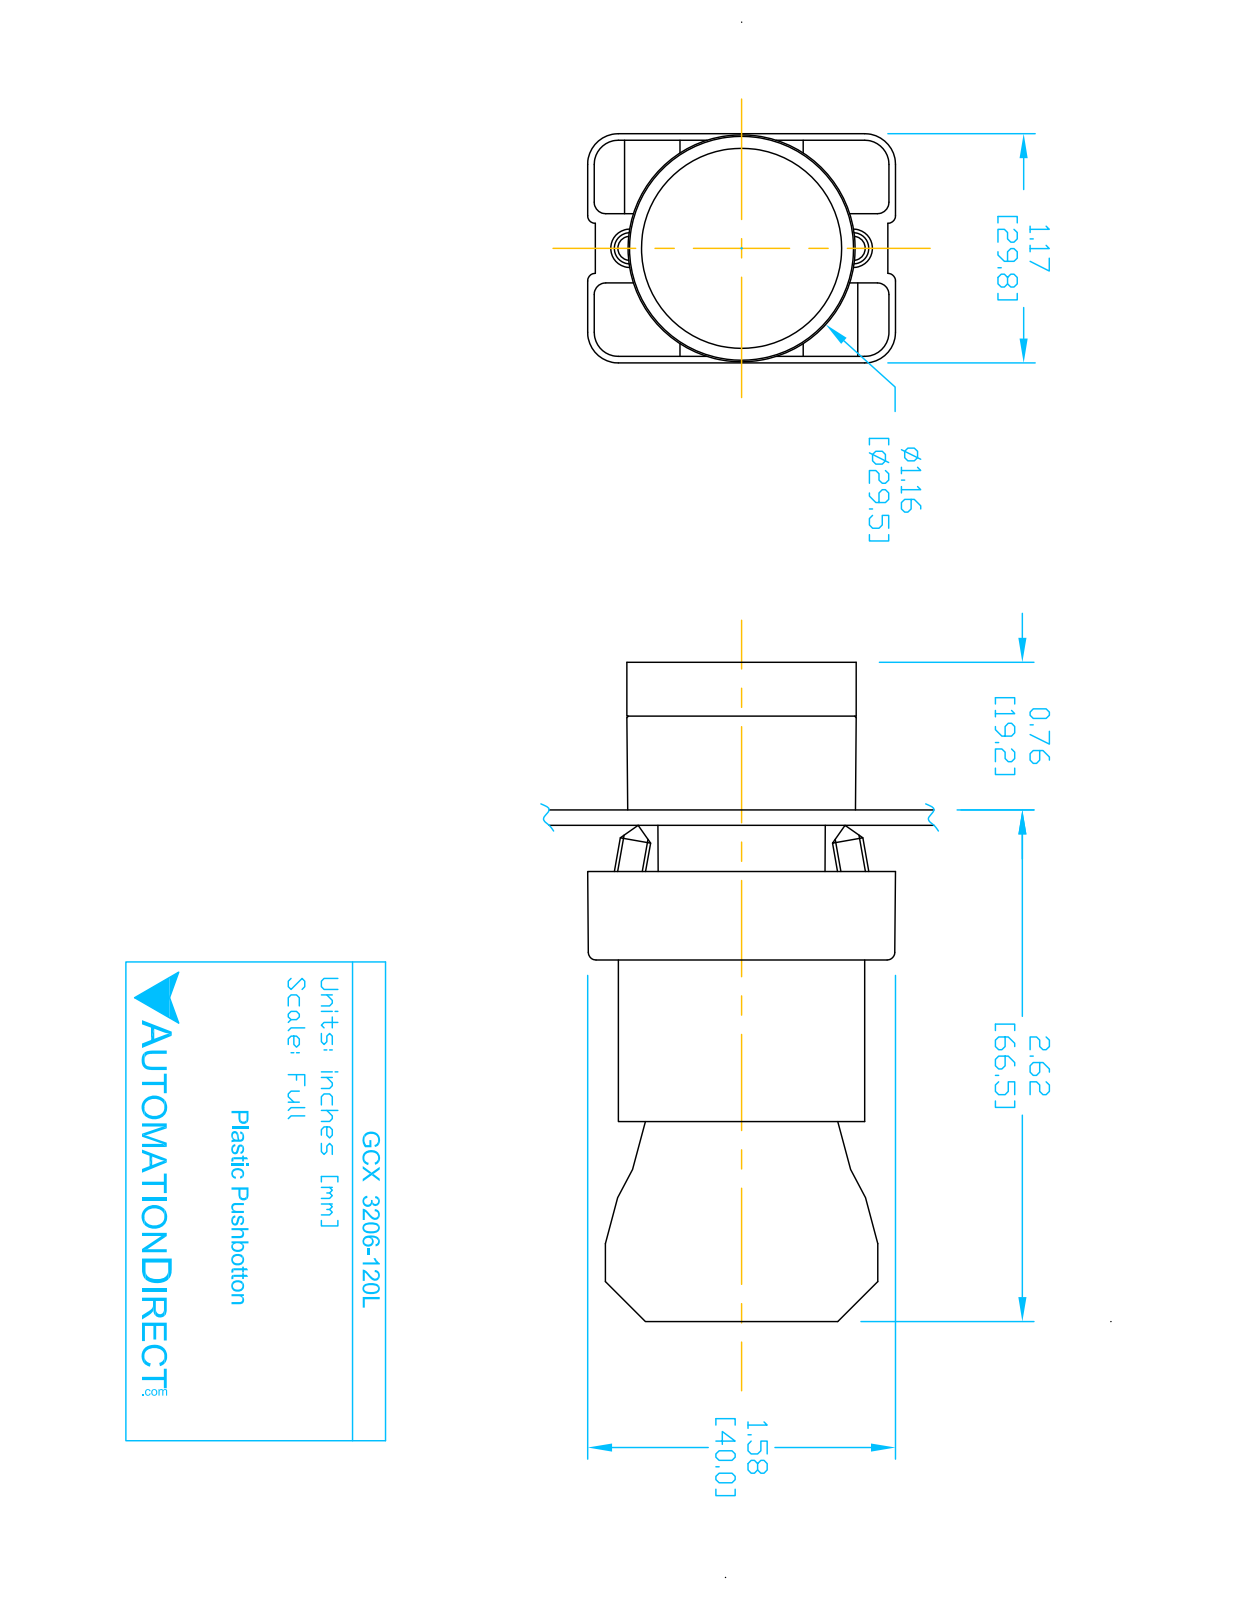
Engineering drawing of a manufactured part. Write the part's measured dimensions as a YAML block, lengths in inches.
part_name: "ecx1040; ECX3029-2; GCX3206-120L; ECX1050 (+1 more)"
step_written_by: "SolidWorks 2016 (AUTOMOTIVE_DESIGN)"
units: inches
bodies: {solids: 8, faces: 431, planar: 252, cylindrical: 148, other: 31}
overall_size: [3.319, 1.581, 1.177]
volume: 2.794
surface_area: 38.77
round_holes:
  - {diameter: 0.079, count: 2}
  - {diameter: 0.124, count: 2}
  - {diameter: 0.13, count: 2}
  - {diameter: 0.087, count: 1}
  - {diameter: 0.197, count: 1}
  - {diameter: 0.469, count: 1}
  - {diameter: 0.878, count: 1}
  - {diameter: 0.888, count: 1}
  - {diameter: 1.024, count: 1}
round_bosses_or_shafts:
  - {diameter: 0.157, count: 4}
  - {diameter: 1.175, count: 1}
  - {diameter: 1.004, count: 1}
  - {diameter: 0.945, count: 1}
  - {diameter: 0.856, count: 1}
  - {diameter: 0.78, count: 1}
  - {diameter: 0.504, count: 1}
partial_cylinders:
  - {radius: 0.059, count: 24}
  - {radius: 0.041, count: 12}
  - {radius: 0.124, count: 12}
  - {radius: 0.157, count: 12}
  - {radius: 0.039, count: 8}
  - {radius: 0.128, count: 2}
  - {radius: 0.02, count: 1}
  - {radius: 0.063, count: 1}
face_to_face_distances: [0.827, 0.579, 2.02, 1.193, 1.171, 0.276, 2.295, 1.469, 0.031, 0.033]
hole_center_spacings: [0.236, 0.544, 0.472, 0.49]
